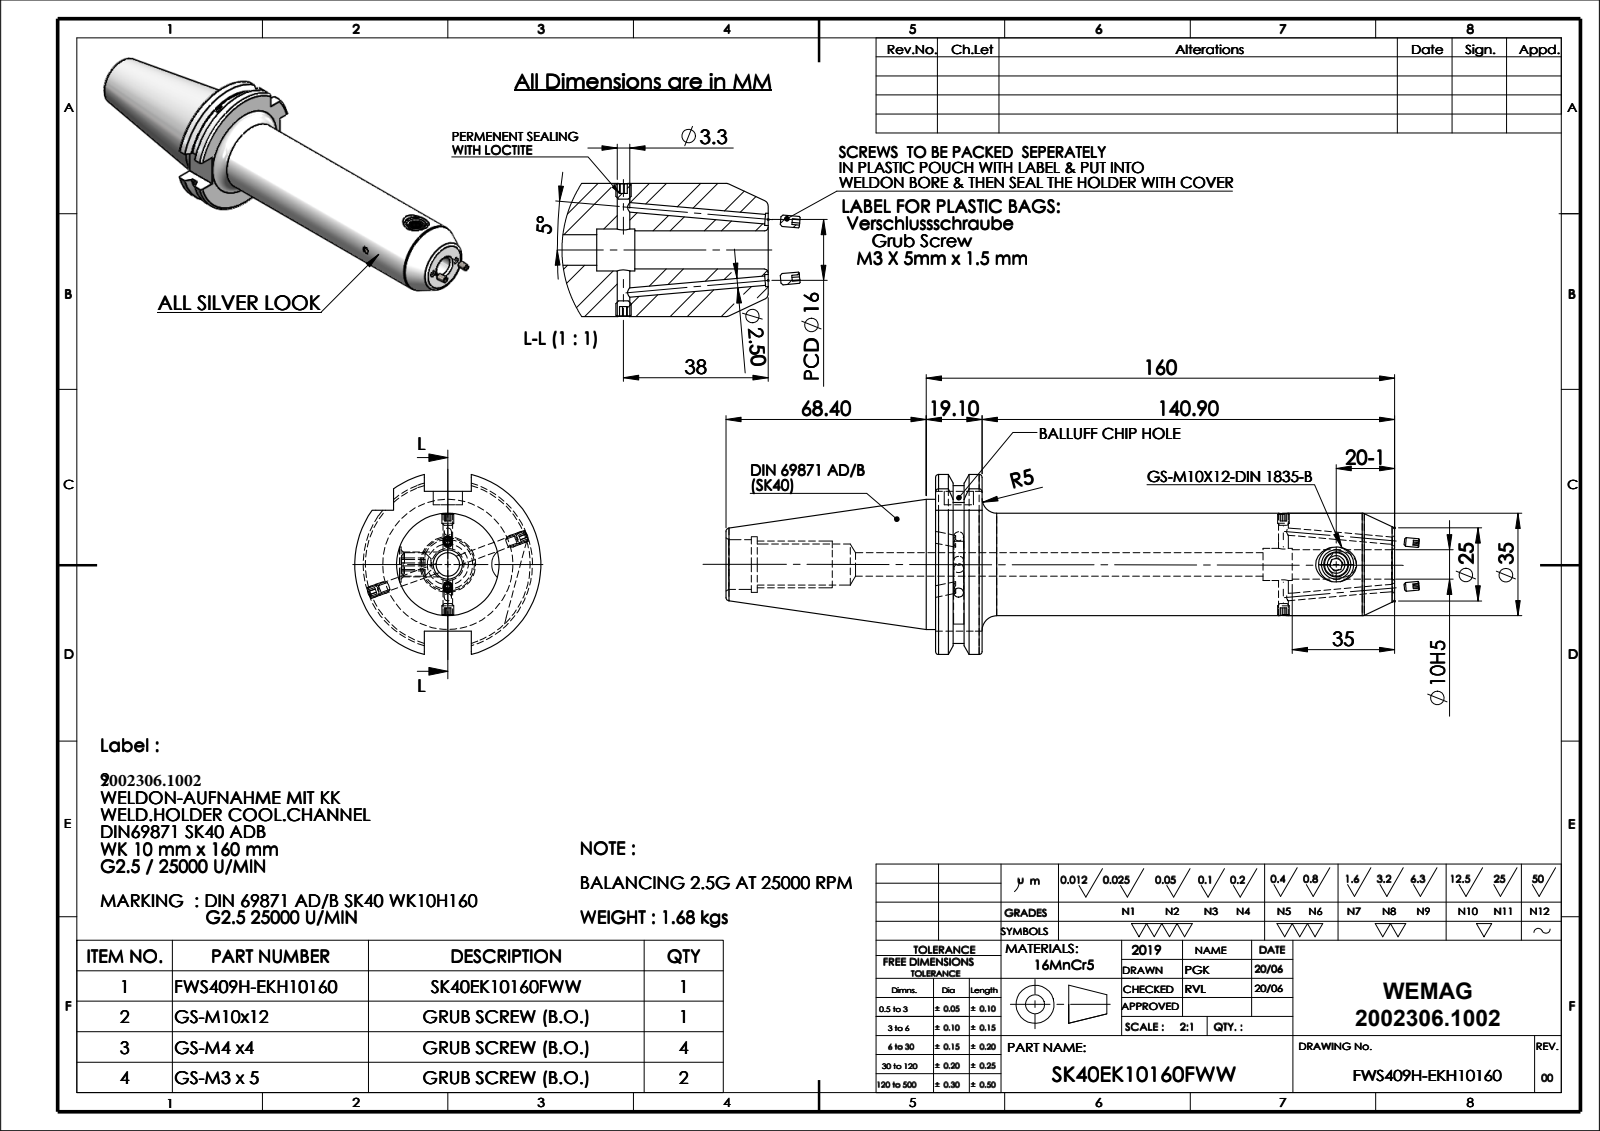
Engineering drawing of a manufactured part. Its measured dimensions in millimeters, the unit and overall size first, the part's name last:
Units: millimetres
Overall size (bounding box): 228.4 × 63.55 × 61.48
Round holes (diameter × count): ⌀2.5 ×2, ⌀3.2 ×2, ⌀3.3 ×2, ⌀10 ×2, ⌀8 ×1, ⌀8.5 ×1, ⌀11 ×1, ⌀12 ×1, ⌀14 ×1, ⌀17 ×1, ⌀19 ×1
Round bosses / shafts (diameter × count): ⌀44.45 ×1, ⌀35 ×1
Partial cylindrical surfaces — rounded edges, fillets, slot ends (radius × count): R28.12 ×1, R31.77 ×1
Main face-to-face distances: 15.9, 156.8, 140.9, 16.1, 47.8, 71.6, 87.5, 228.4, 10.7, 60.9
Hole centre spacings: 110.85
Volume: 226 344 mm³ · Surface area: 40 253 mm²
Bodies: 1 solid, 127 faces (33 planar, 50 cylindrical, 44 other)
Part name (STEP PRODUCT): 91406-WK210160
STEP written by: SolidWorks 2018 (CONFIG_CONTROL_DESIGN)
